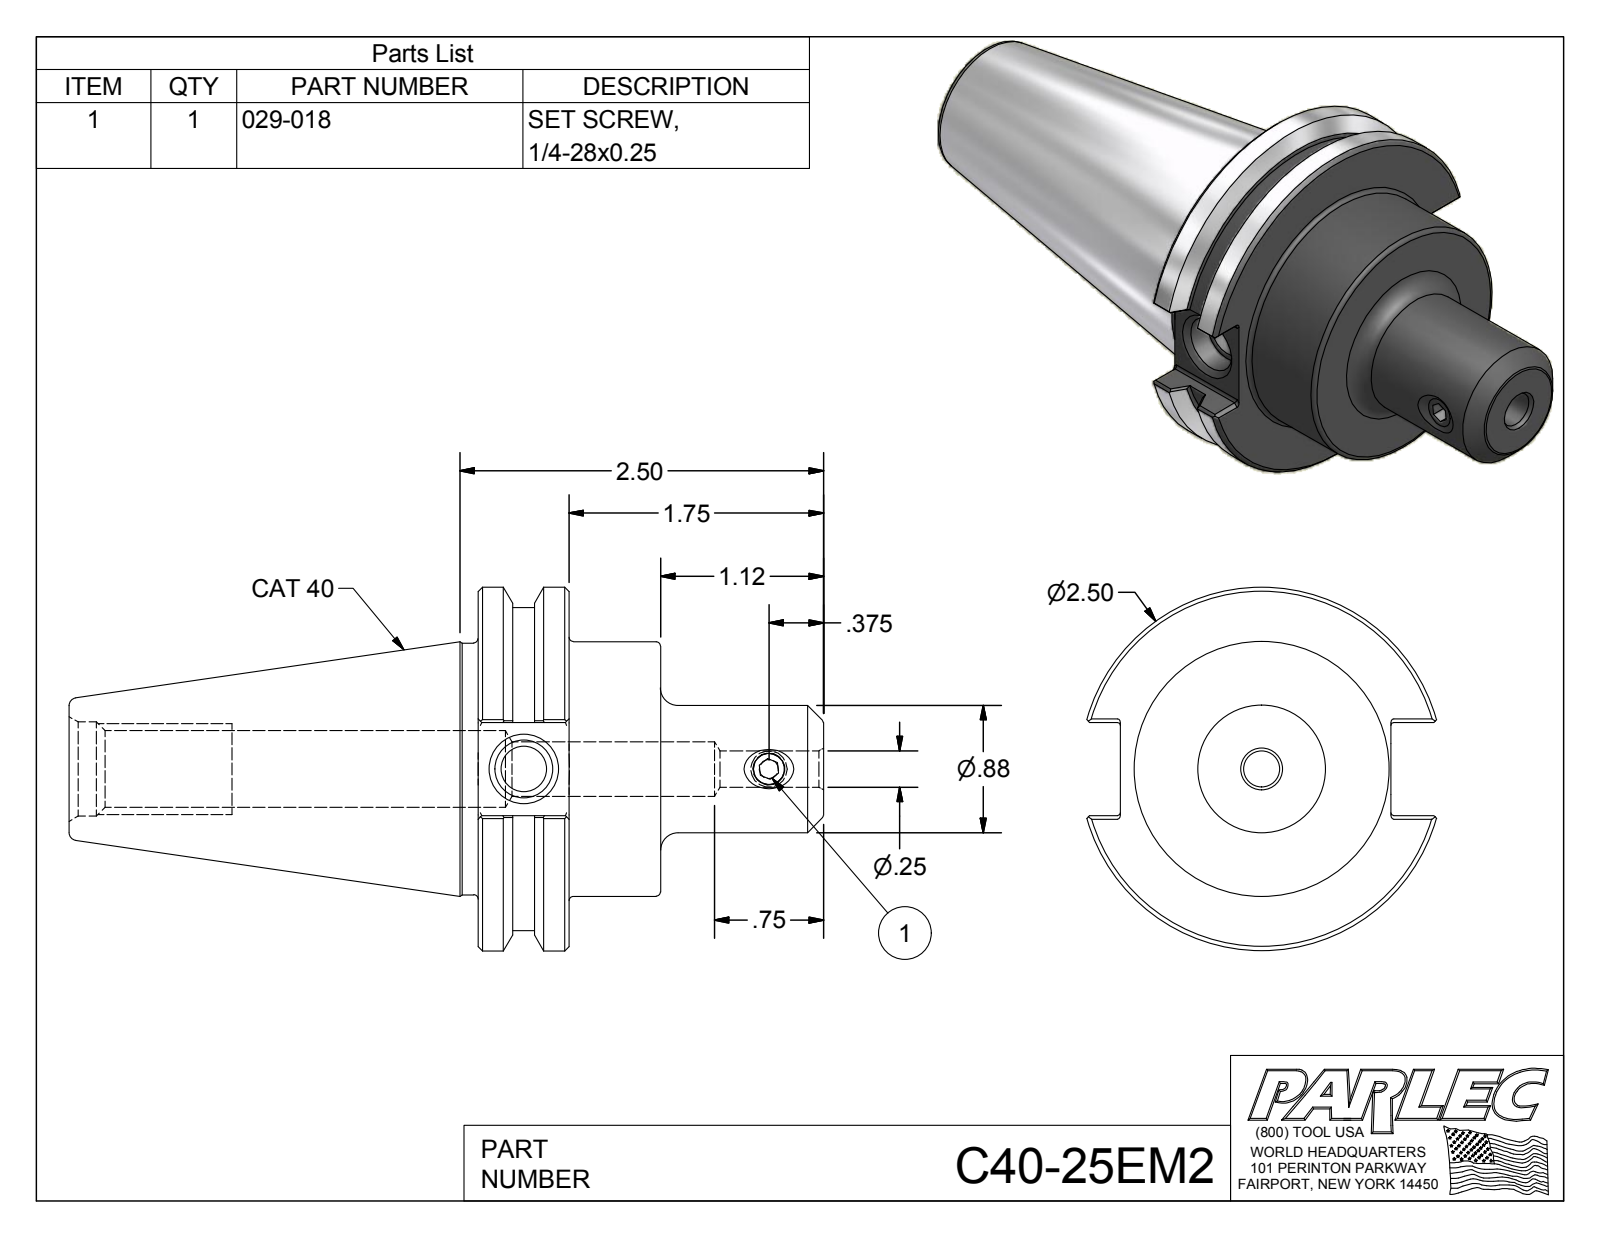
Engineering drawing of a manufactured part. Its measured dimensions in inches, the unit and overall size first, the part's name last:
Units: inches
Overall size (bounding box): 4.938 × 2.5 × 2.417
Round holes (diameter × count): ⌀0.211 ×1, ⌀0.25 ×1, ⌀0.375 ×1, ⌀0.527 ×1, ⌀0.563 ×1, ⌀0.648 ×1
Round bosses / shafts (diameter × count): ⌀2.5 ×1, ⌀2.219 ×1, ⌀1.75 ×1, ⌀0.875 ×1, ⌀0.25 ×1
Main face-to-face distances: 0.625, 0.64, 2.125, 1.5, 2.813, 3.437, 4.937, 1.871, 0.125, 1.323
Hole centre spacings: 1.435
Volume: 6.952 in³ · Surface area: 36.74 in²
Bodies: 2 solids, 58 faces (19 planar, 15 cylindrical, 24 other)
Part name (STEP PRODUCT): C40-25EM2; C40-25EM2-1; 029-018
STEP written by: Autodesk Inventor 2012 (AUTOMOTIVE_DESIGN)
